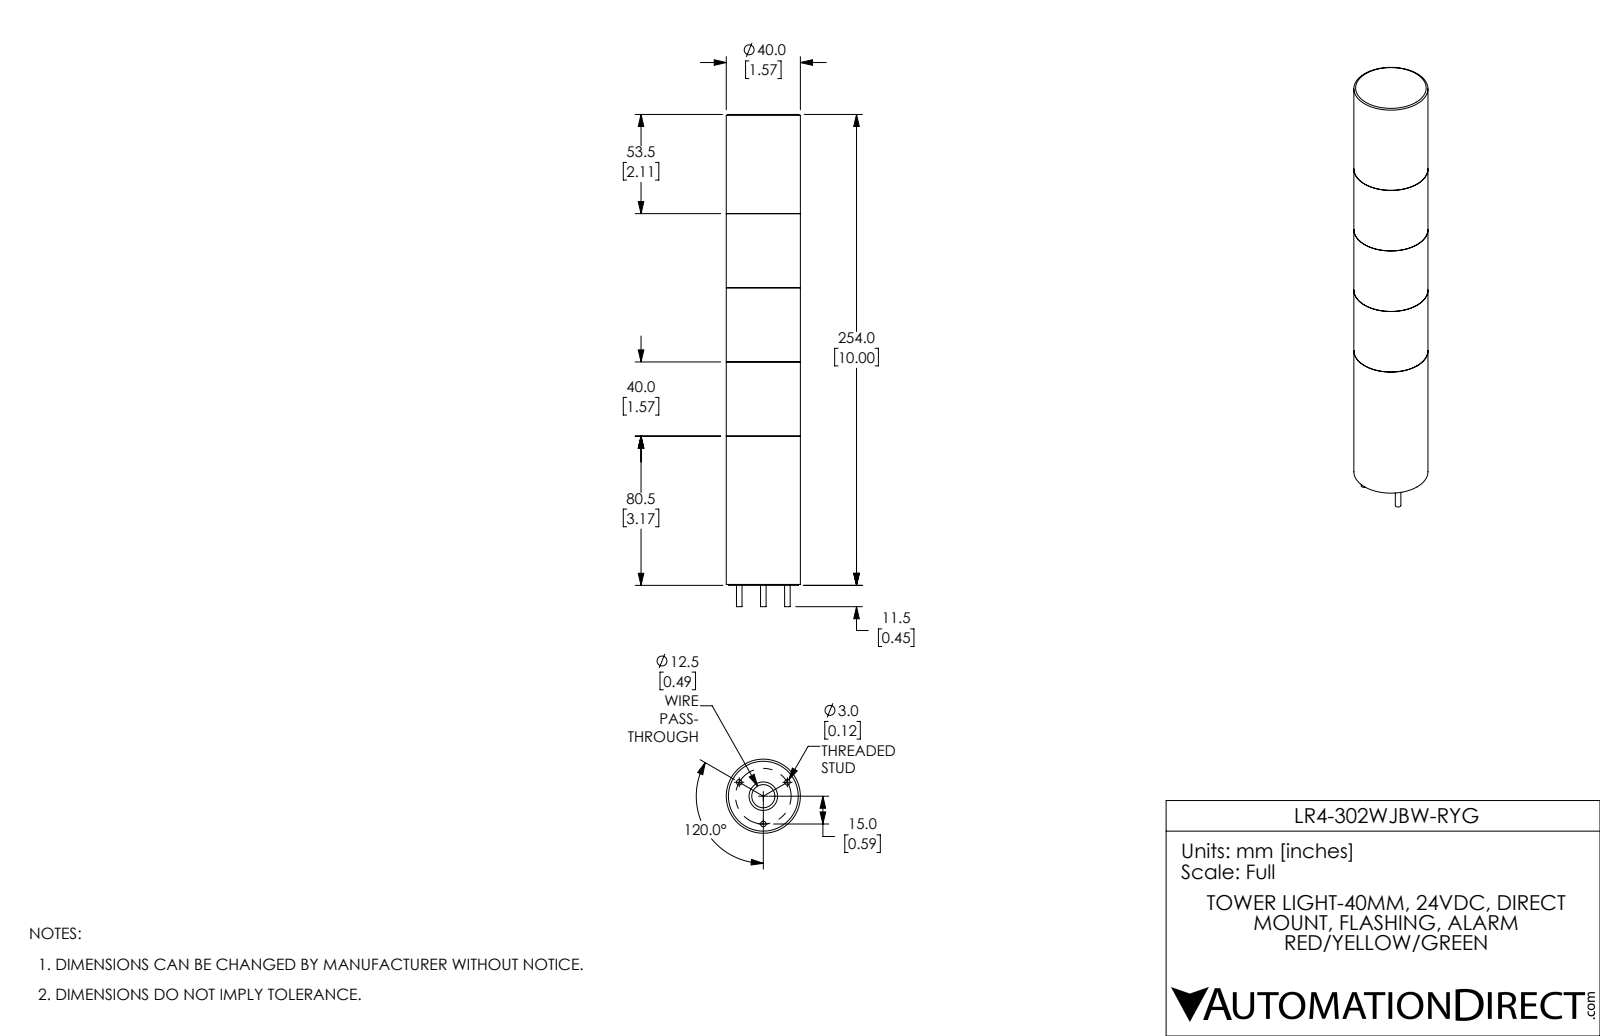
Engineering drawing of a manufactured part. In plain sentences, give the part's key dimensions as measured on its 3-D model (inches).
The part is named "LR4-302WJBW-RYG". Its 3-D file was written by "SolidWorks 2017 (AUTOMOTIVE_DESIGN)". It is 5 solids with 85 faces: 31 planar, 52 cylindrical and 2 other. Overall it measures 10.453 by 1.575 by 1.575 inches. Its volume is 19.35 cubic inches and its surface area 84.18 square inches. Round holes: 1 of diameter 0.492, 1 of diameter 0.606, 1 of diameter 1.386, 1 of diameter 1.463, 1 of diameter 1.476. Round bosses or shafts: 3 of diameter 0.118, 1 of diameter 1.575, 1 of diameter 1.484, 1 of diameter 1.461, 1 of diameter 1.366. The main face-to-face distances are 1.575, 3.15, 3.276, 4.724, 1.701, 4.85, 0.406, 6.425, 1.98, 3.555.
